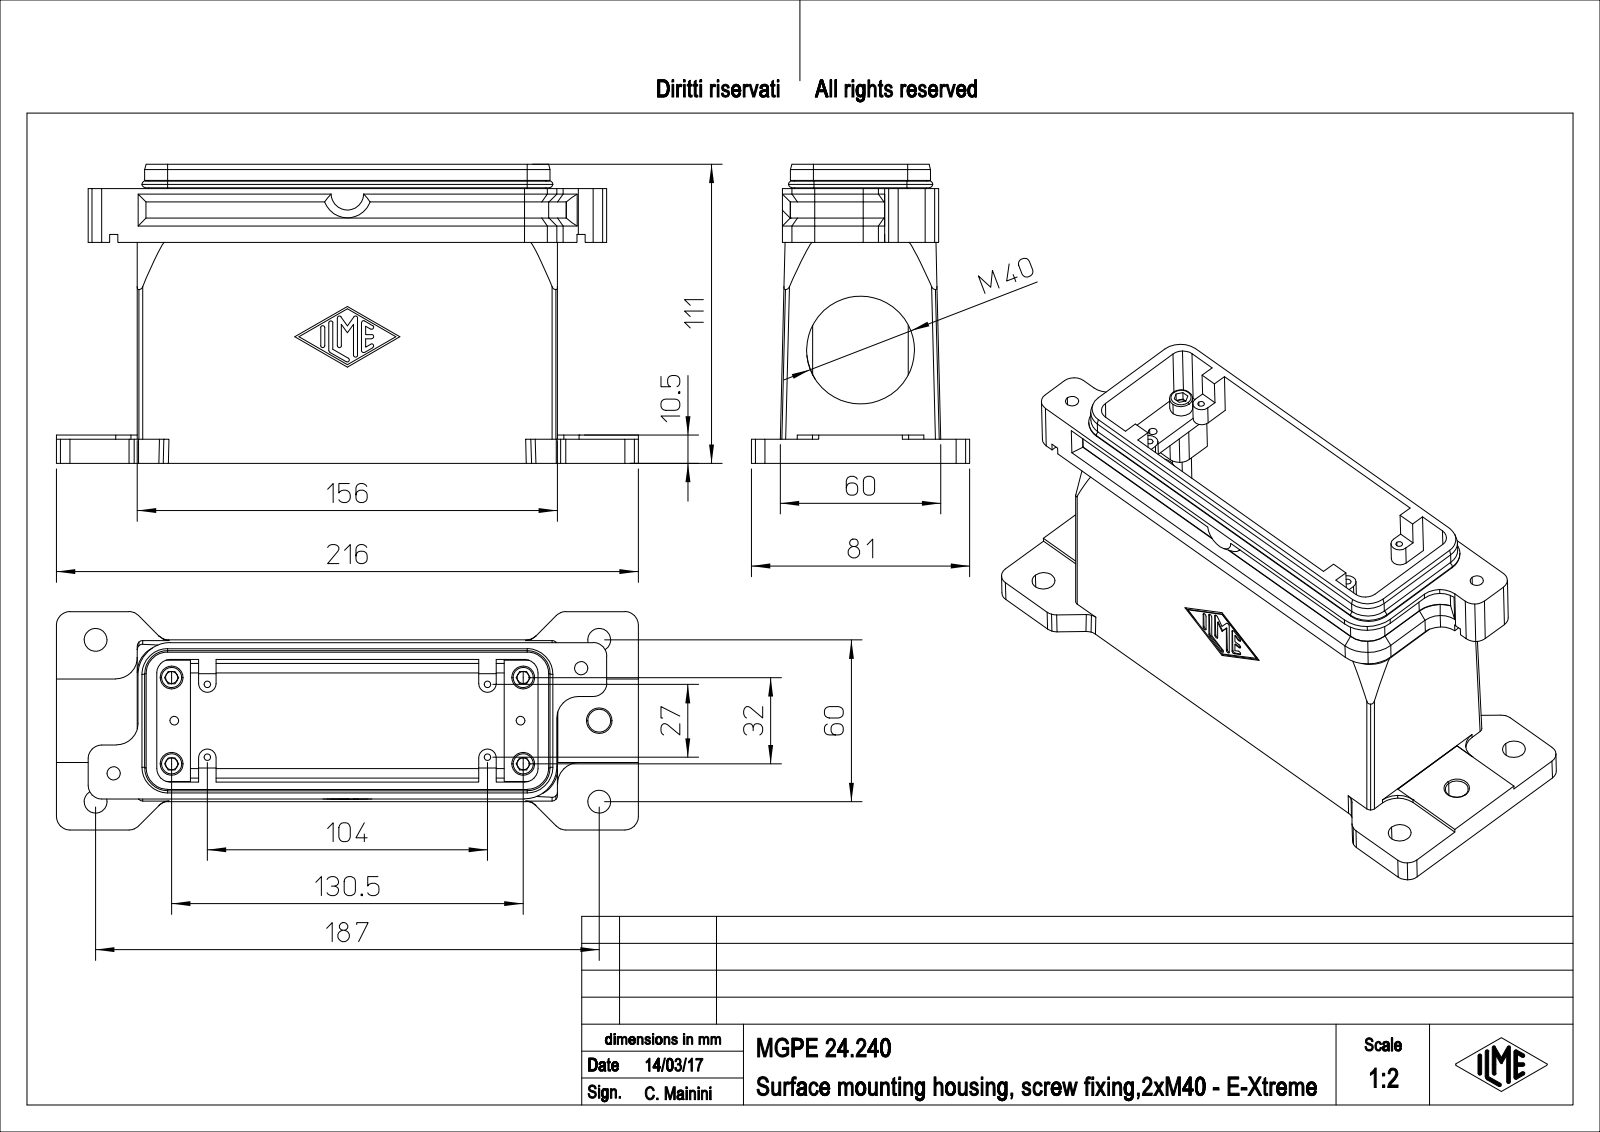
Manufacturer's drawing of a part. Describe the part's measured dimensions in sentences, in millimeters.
The part is named "MGPE_24.240". Its 3-D file was written by "PTC Creo Elements/Direct Modeling 19.0E 27-Jun-2016 (C) Parametric Technology GmbH (AUTOMOTIVE_DESIGN)". It is 1 solid with 571 faces: 275 planar, 220 cylindrical and 76 other. Overall it measures 216 by 111 by 81 millimeters. Its volume is 387 452 cubic millimeters and its surface area 127 671 square millimeters. Round holes: 6 of diameter 8.5, 4 of diameter 2.46, 4 of diameter 4.13, 4 of diameter 5.5, 2 of diameter 3.24, 2 of diameter 4.92, 2 of diameter 14, 1 of diameter 40. Round bosses or shafts: 4 of diameter 8.5, 4 of diameter 5, 4 of diameter 2.5. Partial cylindrical surfaces (rounded edges, fillets, slot ends): 32 of radius 5, 14 of radius 0.75, 6 of radius 8, 4 of radius 1.5, 4 of radius 2, 4 of radius 3.25, 4 of radius 7, 4 of radius 8.5. The main face-to-face distances are 45.5, 10, 9, 3, 102, 1, 3.25, 5.5, 6.25, 51.75. The hole center spacings are 13.48, 16.03, 18.23, 30, 31.53, 32.34, 32.47, 41.9.
